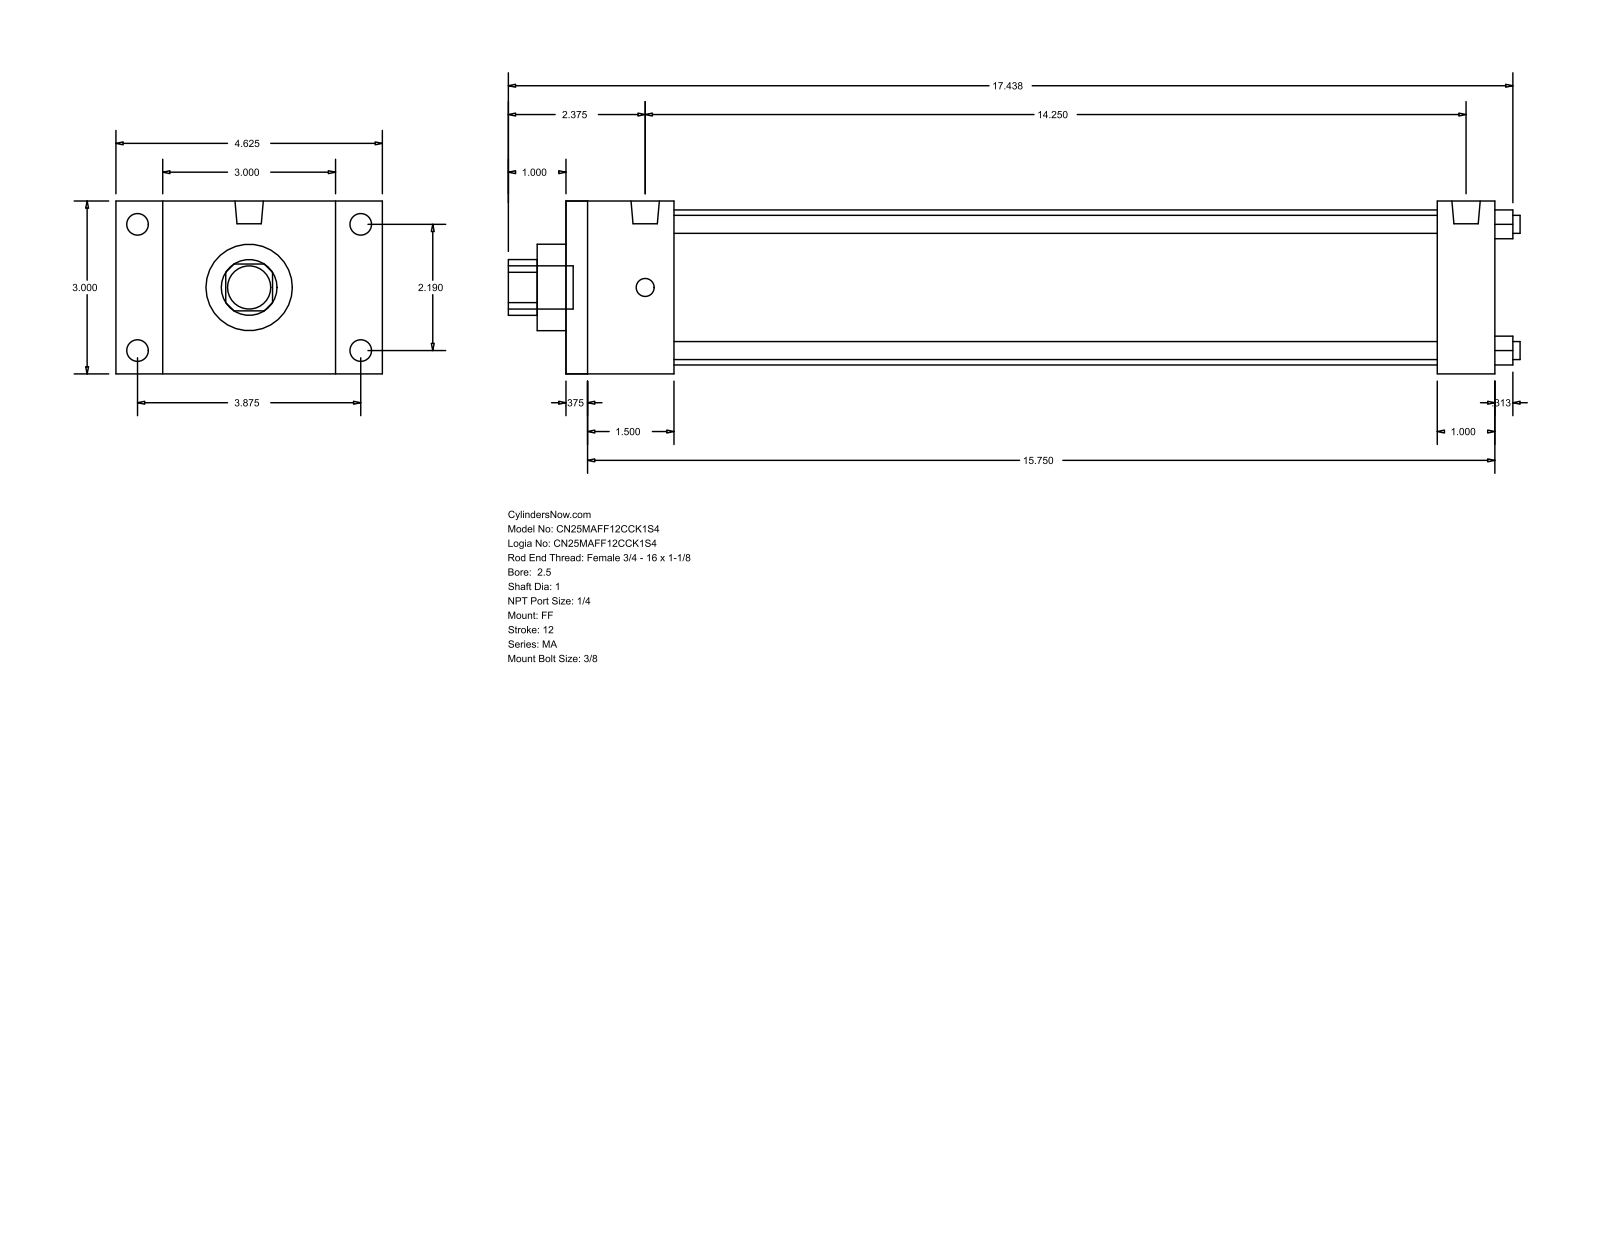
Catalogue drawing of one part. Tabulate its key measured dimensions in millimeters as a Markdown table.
| quantity | value |
| --- | --- |
| part name | MA_FF__0250_1 |
| STEP written by | GSSL Pune (CONFIG_CONTROL_DESIGN) |
| units | millimeters |
| bodies | 0 solids, 92 faces (64 planar, 28 cylindrical, 0 other) |
| overall size | 446.09 × 117.47 × 76.2 |
| round holes (diameter × count) | 7.94 × 4, 25.4 × 1, 38.1 × 1, 68.33 × 1 |
| round bosses / shafts (diameter × count) | 9.53 × 4, 7.94 × 4, 12.49 × 2, 19.05 × 1 |
| partial cylindrical surfaces (radius × count) | 12.29 × 1 |
| main face-to-face distances | 76.2, 409.58, 9.52, 400.06, 47.63, 384.17, 38.11, 374.65, 336.54, 361.95 |
| hole center spacings | 39.33, 55.62, 78.66 |
